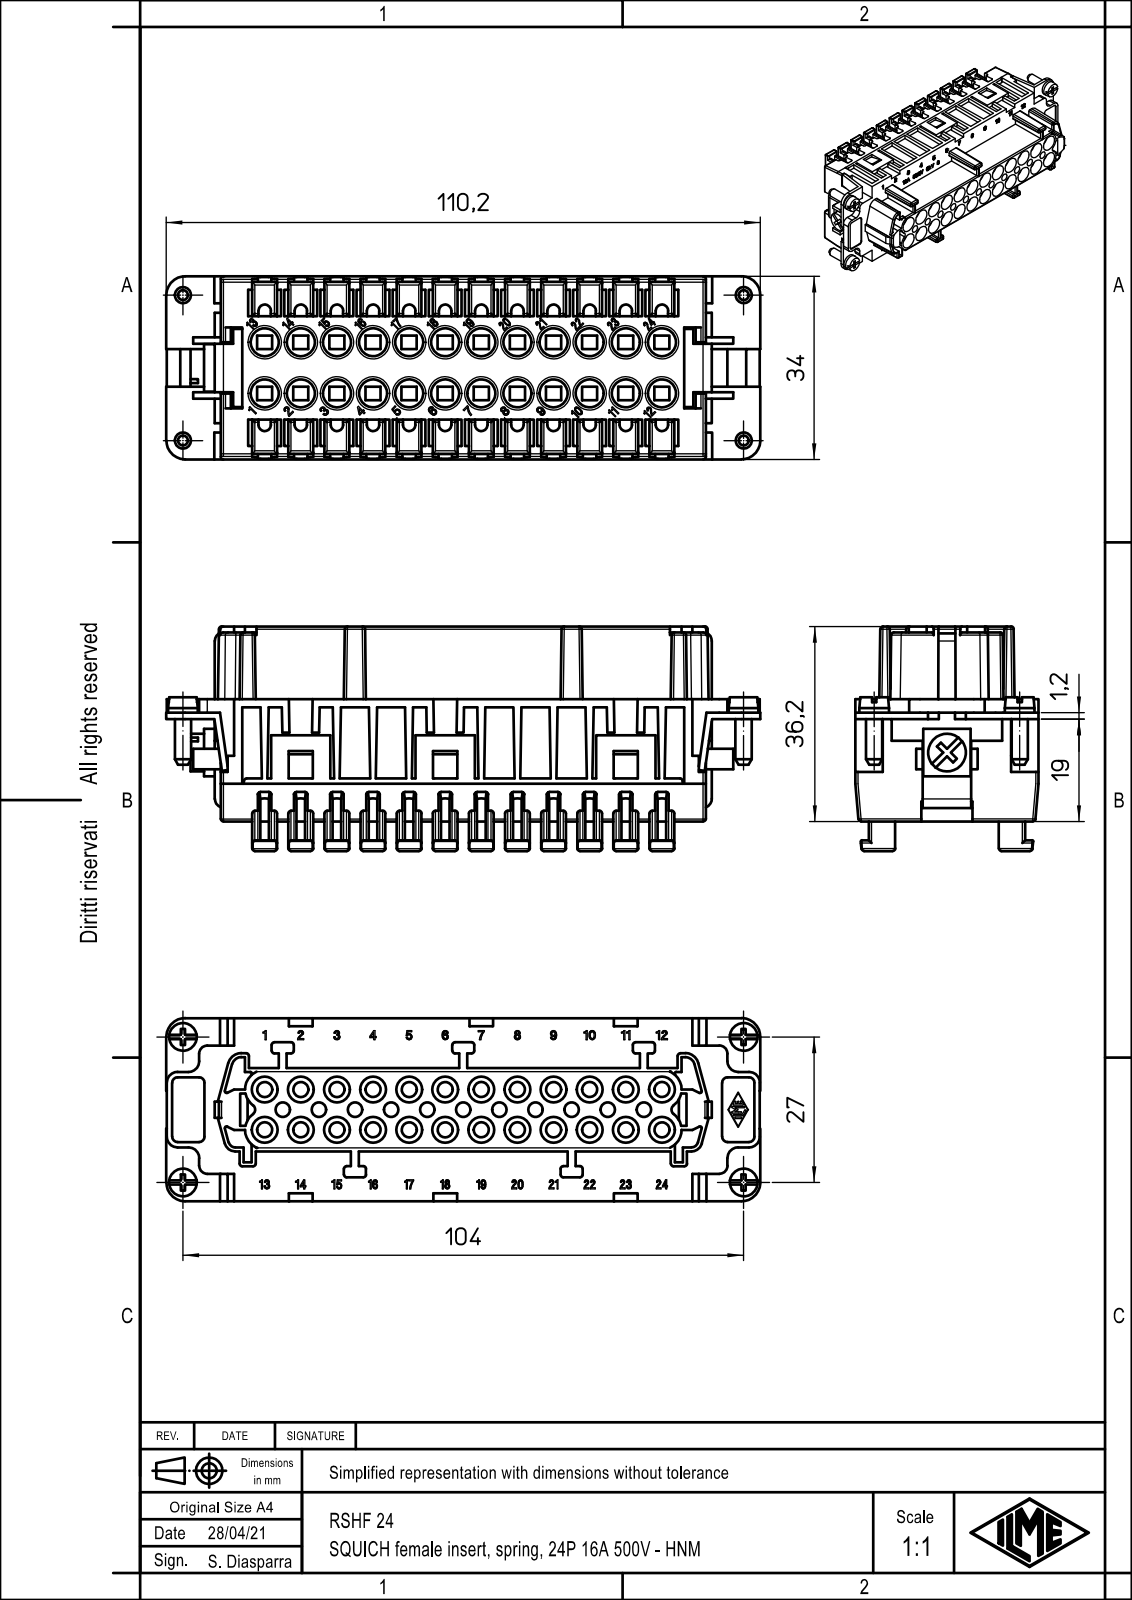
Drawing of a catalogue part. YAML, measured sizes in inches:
part_name: "RSHF_24"
step_written_by: "Creo Elements/Direct Modeling 20.1B 02-Apr-2019 (C) Parametric Technology GmbH (AUTOMOTIVE_DESIGN)"
units: inches
bodies: {solids: 1, faces: 2909, planar: 1703, cylindrical: 864, other: 342}
overall_size: [4.339, 1.642, 1.339]
volume: 4.91
surface_area: 52.87
round_holes:
  - {diameter: 0.11, count: 24}
  - {diameter: 0.205, count: 24}
  - {diameter: 0.228, count: 24}
  - {diameter: 0.106, count: 11}
  - {diameter: 0.13, count: 1}
round_bosses_or_shafts:
  - {diameter: 0.217, count: 4}
  - {diameter: 0.118, count: 4}
  - {diameter: 0.276, count: 1}
partial_cylinders:
  - {radius: 0.02, count: 234}
  - {radius: 0.012, count: 56}
  - {radius: 0.008, count: 50}
  - {radius: 0.045, count: 24}
  - {radius: 0.039, count: 12}
  - {radius: 0.079, count: 10}
  - {radius: 0.059, count: 4}
  - {radius: 0.067, count: 4}
face_to_face_distances: [0.059, 1.28, 0.894, 0.528, 0.531, 0.098, 0.264, 0.791, 1.22, 1.319]
hole_center_spacings: [0.264, 0.457, 0.528, 0.647, 0.791, 0.875, 1.055, 1.119]
